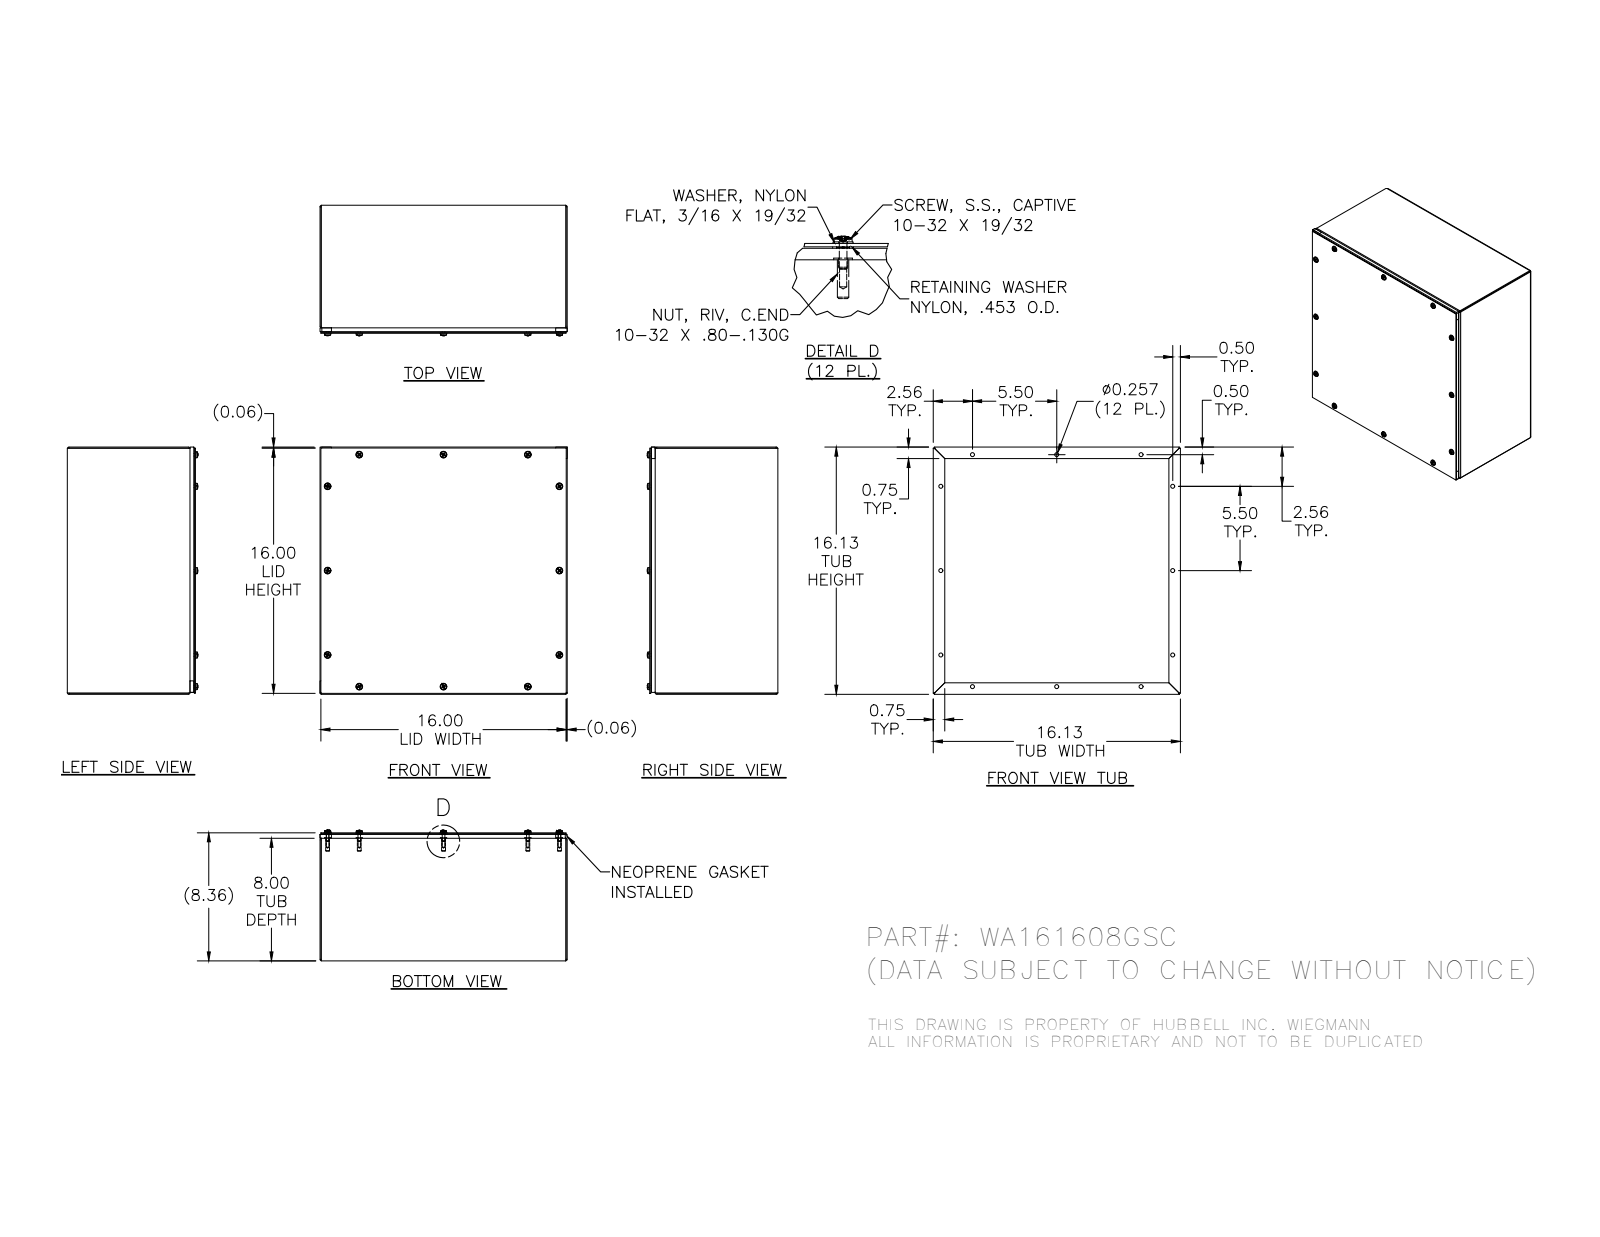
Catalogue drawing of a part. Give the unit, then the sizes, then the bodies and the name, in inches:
Units: inches
Overall size (bounding box): 16.125 × 16.125 × 8.511
Round holes (diameter × count): ⌀0.188 ×12, ⌀0.257 ×12, ⌀0.278 ×12, ⌀0.281 ×12, ⌀0.156 ×11, ⌀0.196 ×11
Round bosses / shafts (diameter × count): ⌀0.453 ×12, ⌀0.437 ×12, ⌀0.167 ×12, ⌀0.406 ×11, ⌀0.248 ×11
Partial cylindrical surfaces — rounded edges, fillets, slot ends (radius × count): R0.089 ×12, R0.031 ×8, R0.105 ×8
Main face-to-face distances: 0.074, 8.282, 16.051, 8.356, 8.208, 16.125, 15.977, 0.356, 7.926, 0.282
Hole centre spacings: 5.5, 15.094, 13.224, 7.839, 11, 15.093, 7.839, 16.094
Volume: 88.09 in³ · Surface area: 2 262 in²
Bodies: 53 solids, 1258 faces (590 planar, 328 cylindrical, 340 other)
Part name (STEP PRODUCT): WA161608GSCBKP; 37210; 39077; 39035 (+3 more)
STEP written by: SolidWorks 2014 (AUTOMOTIVE_DESIGN)
